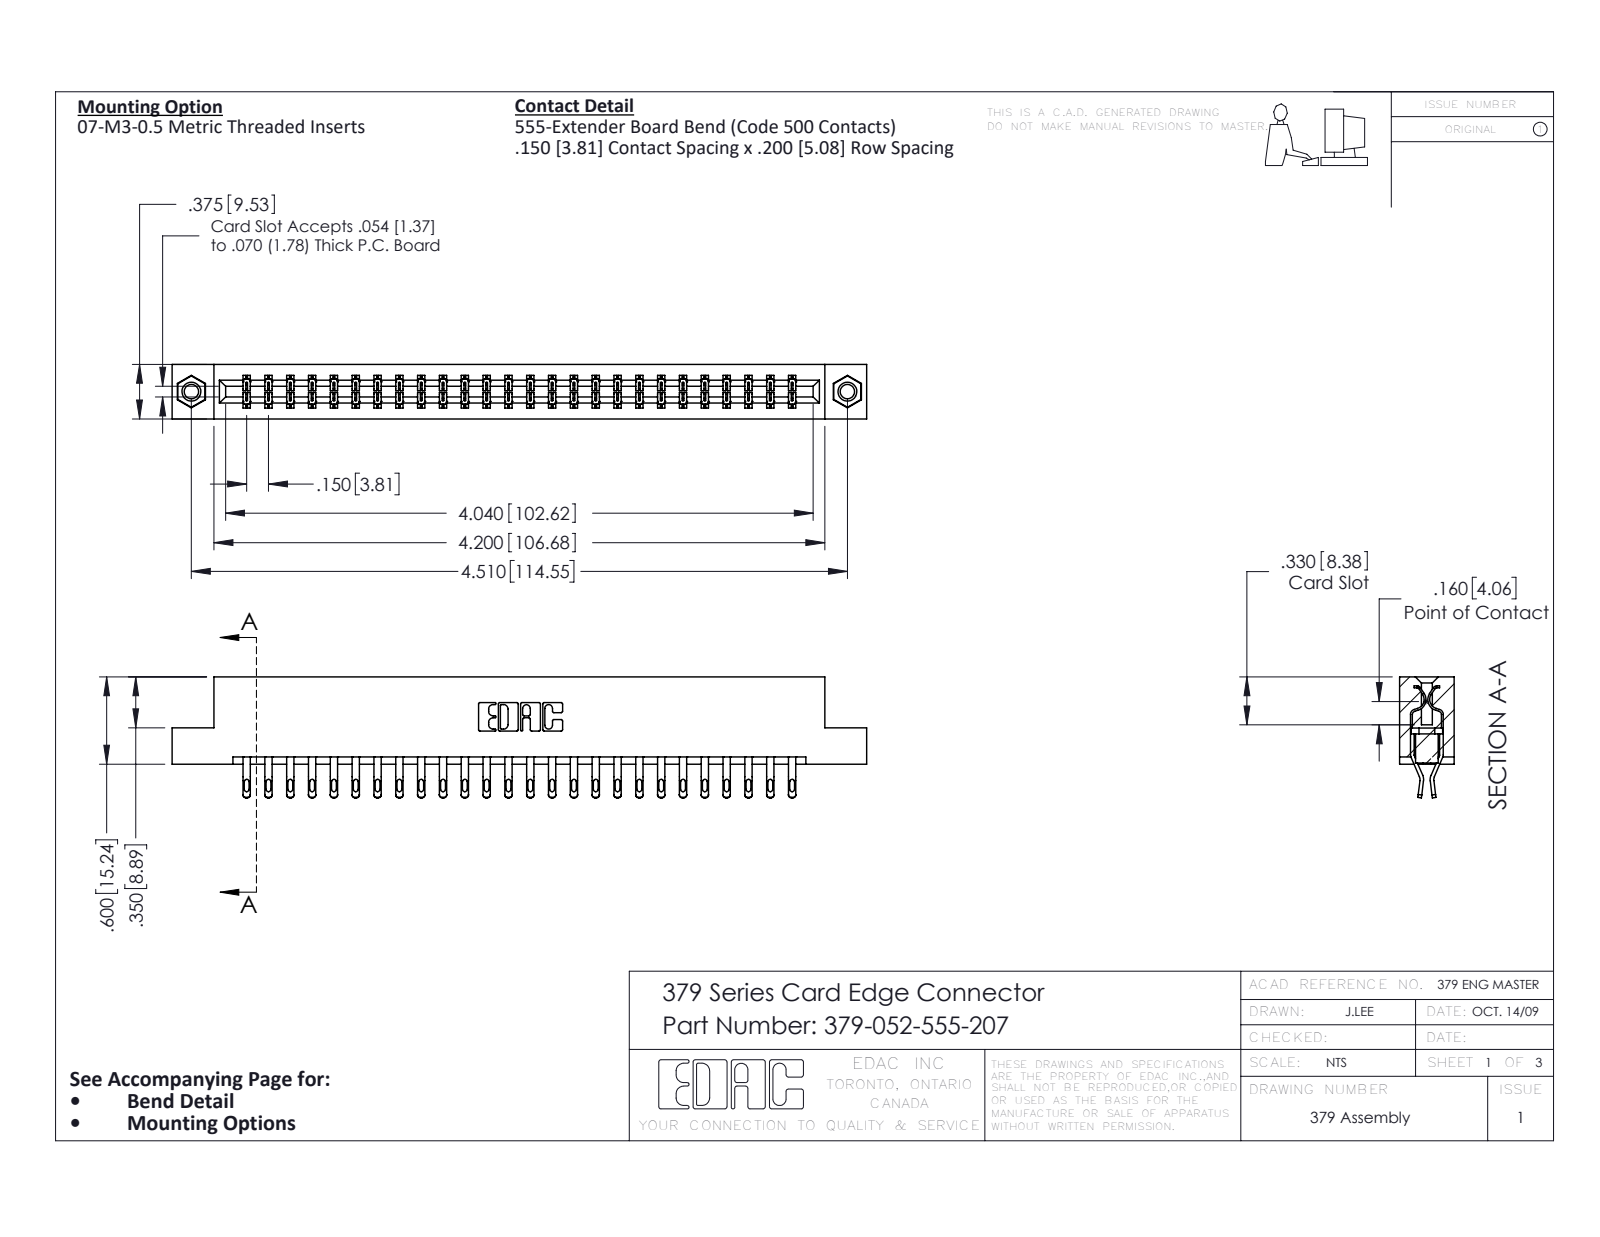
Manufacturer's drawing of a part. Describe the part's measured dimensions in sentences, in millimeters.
The part is named "379-052-555-207; 345-250-001_345-250-005-103; 379 Part_Flush - .156 Dia - TI; 345-292-001_555 Tail". Its 3-D file was written by "SolidWorks 2016 (CONFIG_CONTROL_DESIGN)". It is 55 solids with 3190 faces: 1870 planar, 1304 cylindrical and 16 other. Overall it measures 121.3 by 21.1 by 9.5 millimeters. Its volume is 12 900 cubic millimeters and its surface area 14 900 square millimeters. Round holes: 2 of diameter 2.5, 2 of diameter 3.2, 2 of diameter 4. Round bosses or shafts: 2 of diameter 3.9. Partial cylindrical surfaces (rounded edges, fillets, slot ends): 104 of radius 0.4, 104 of radius 0.5, 78 of radius 0.2, 22 of radius 0.3, 6 of radius 0.2, 6 of radius 0.8, 3 of radius 0.7, 2 of radius 0.3. The main face-to-face distances are 7.6, 1.9, 9.5, 5.1, 5.7, 3.8, 2.5, 15.2, 0.6, 1.9. The hole center spacings are 114.6.
